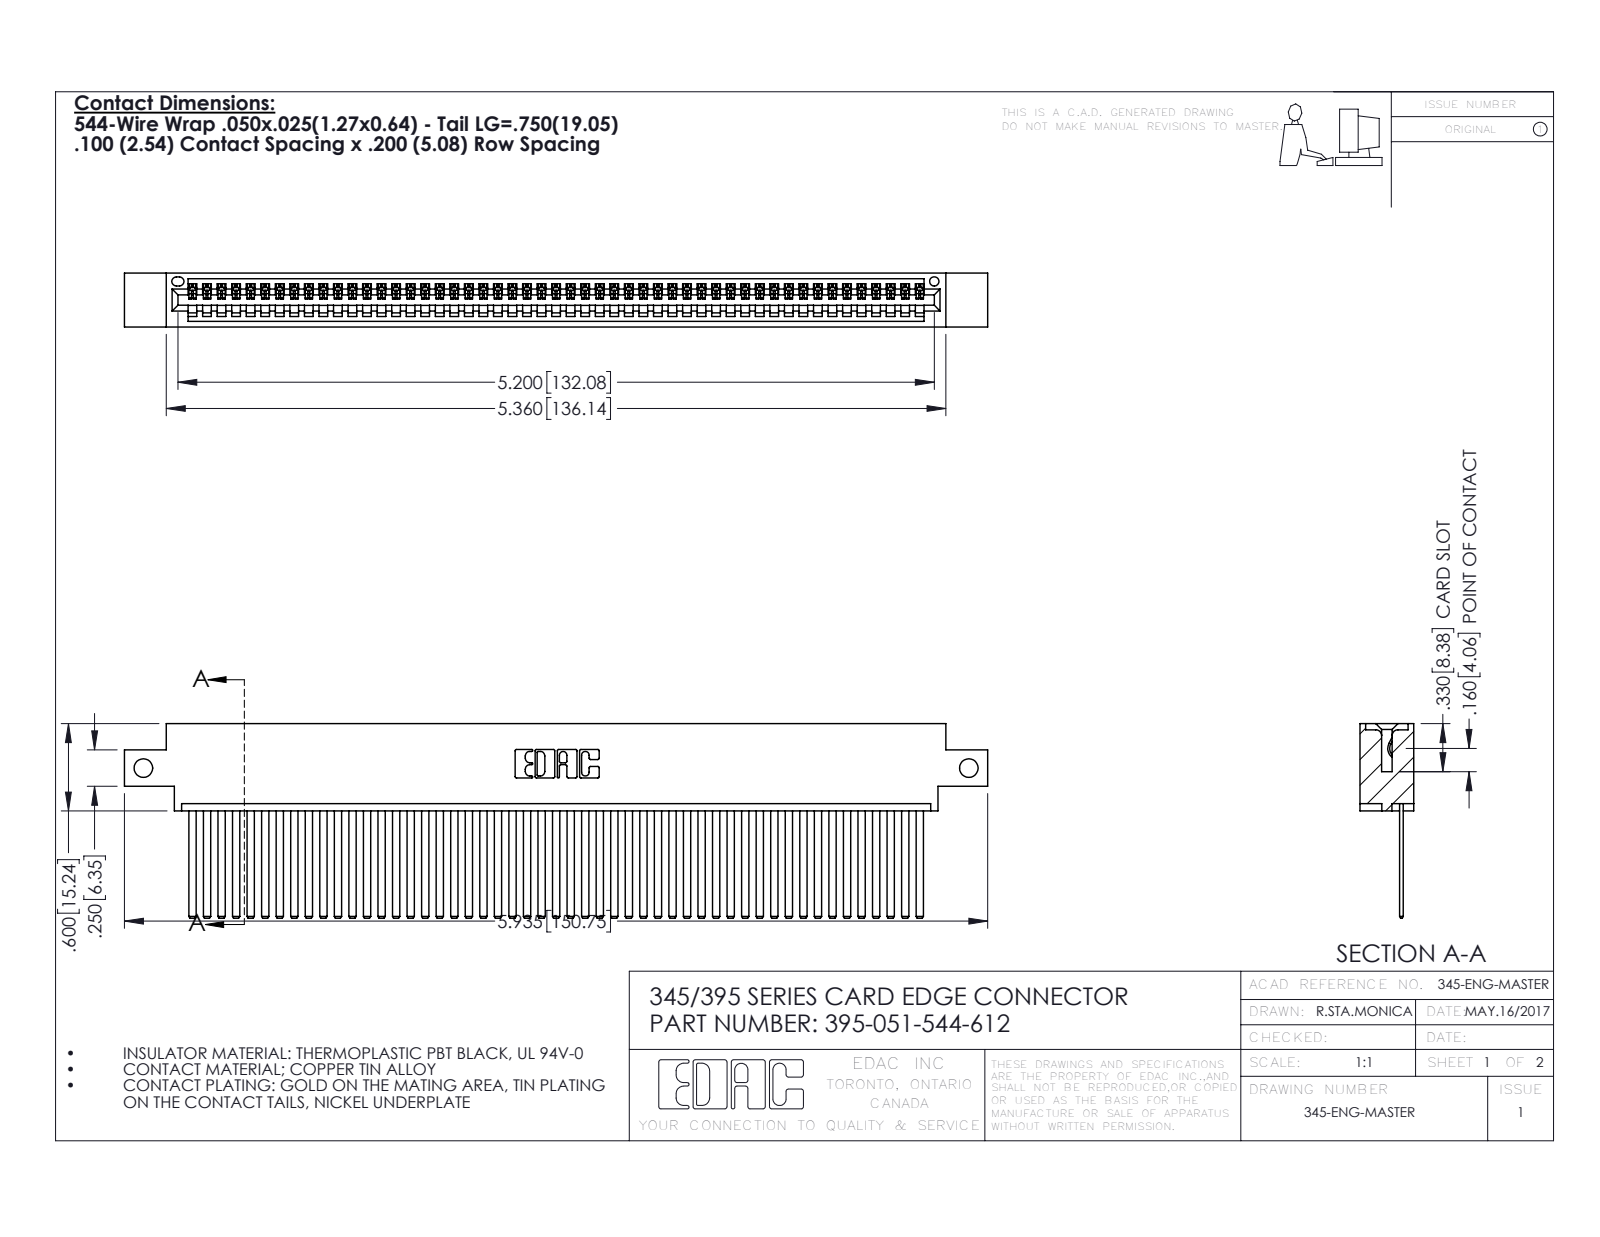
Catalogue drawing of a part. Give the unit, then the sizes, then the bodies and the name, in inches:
Units: inches
Overall size (bounding box): 5.935 × 1.337 × 0.37
Round holes (diameter × count): ⌀0.128 ×2, ⌀0.064 ×1
Partial cylindrical surfaces — rounded edges, fillets, slot ends (radius × count): R0.006 ×102, R0.01 ×22, R0.007 ×6, R0.031 ×6, R0.026 ×3, R0.031 ×2, R0.04 ×2, R0.014 ×1
Main face-to-face distances: 0.072, 0.298, 0.025, 0.098, 0.272, 0.37, 0.2, 0.225, 0.175, 0.149
Hole centre spacings: 5.675
Volume: 0.902 in³ · Surface area: 33.36 in²
Bodies: 52 solids, 2782 faces (1920 planar, 862 cylindrical, 0 other)
Part name (STEP PRODUCT): 395-051-544-612; 345 Part_0.170 Offset - Side Mount; 345-292-001_345-293-144
STEP written by: SolidWorks 2016 (CONFIG_CONTROL_DESIGN)
